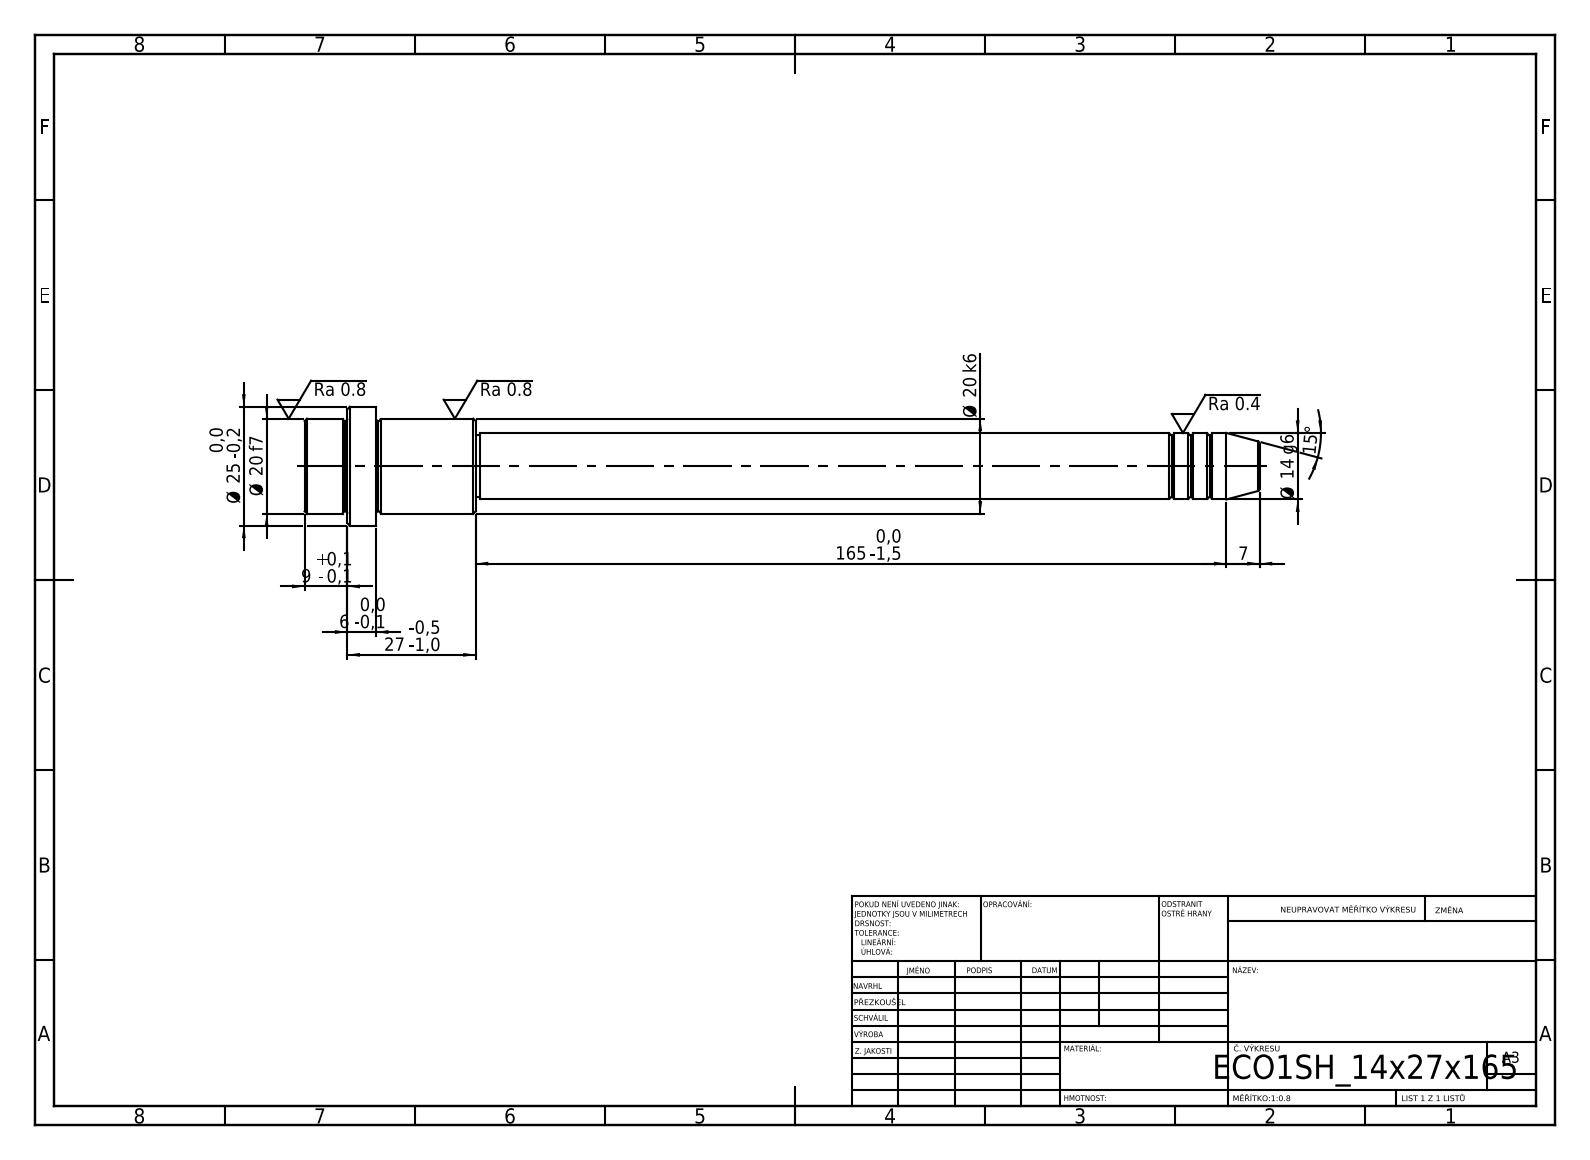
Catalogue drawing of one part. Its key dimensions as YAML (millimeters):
step_written_by: "SolidWorks 2019 (CONFIG_CONTROL_DESIGN)"
units: millimeters
bodies: {solids: 1, faces: 52, planar: 6, cylindrical: 16, other: 30}
overall_size: [201, 25, 25]
volume: 37361
surface_area: 10598
round_bosses_or_shafts:
  - {diameter: 25, count: 1}
  - {diameter: 20, count: 1}
  - {diameter: 14, count: 1}
  - {diameter: 13, count: 1}
face_to_face_distances: [15, 21, 36, 27, 6, 9, 165, 186, 192, 201]
